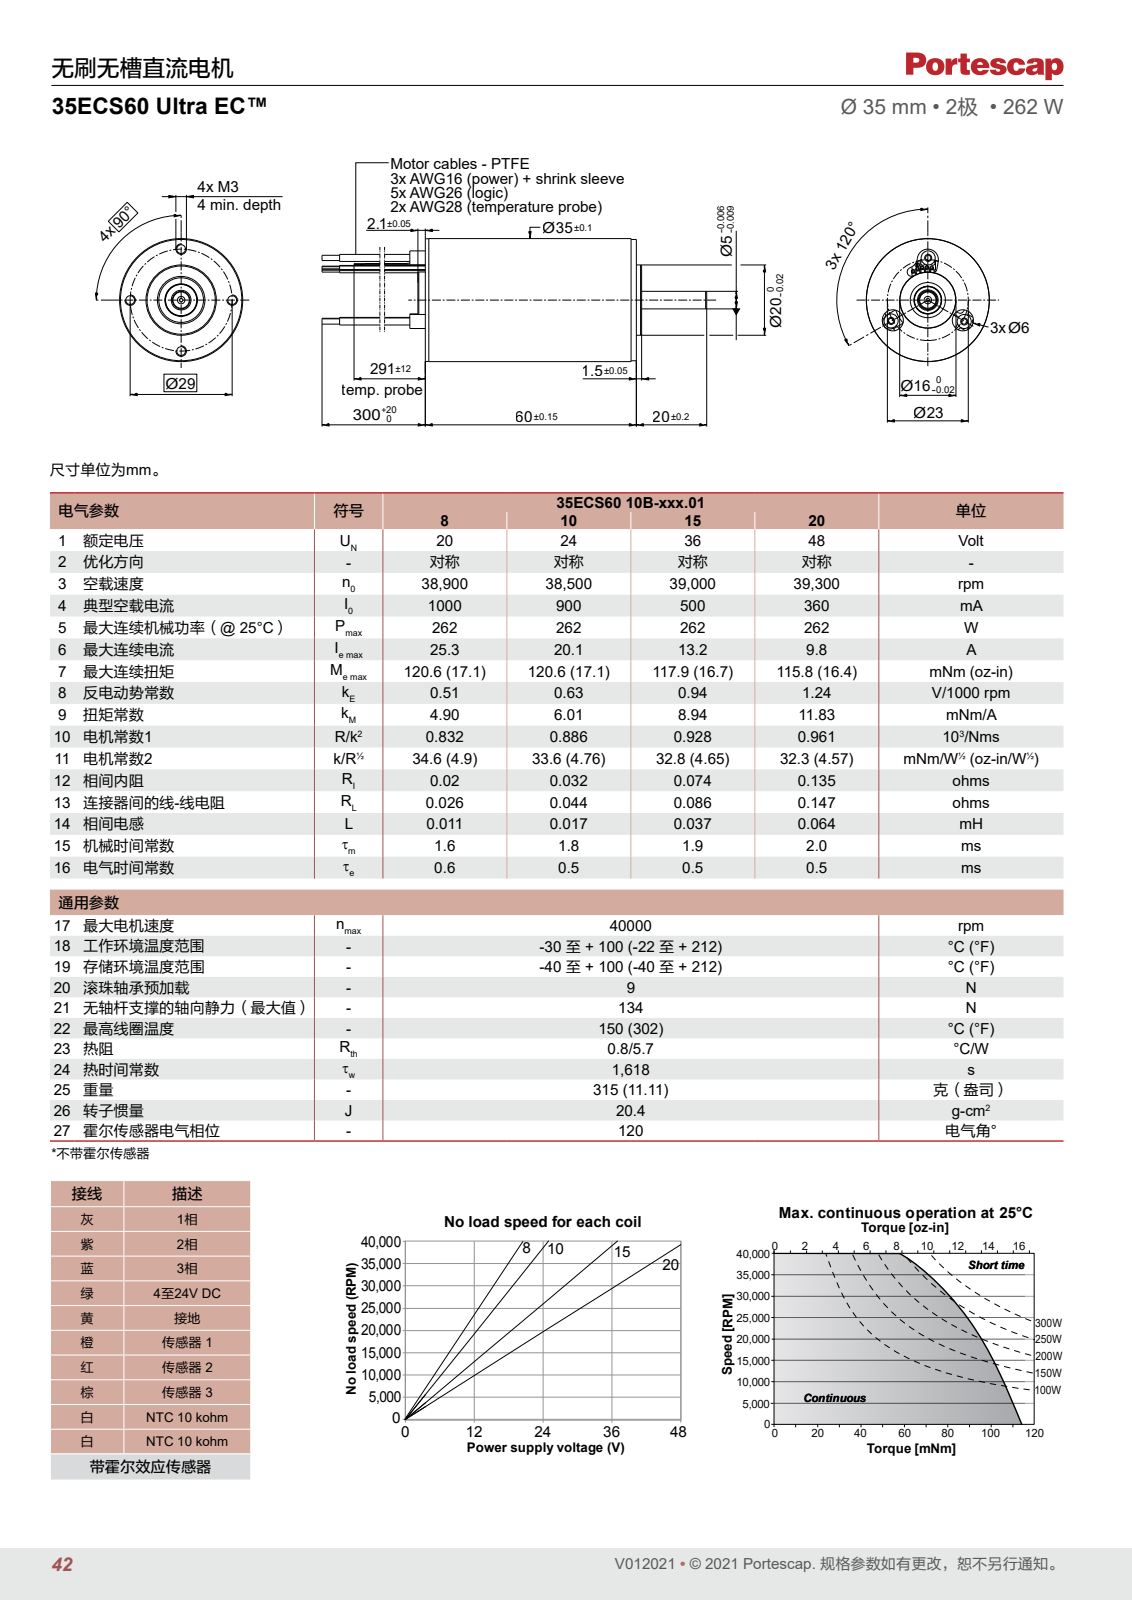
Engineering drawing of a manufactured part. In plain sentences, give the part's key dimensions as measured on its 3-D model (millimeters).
The part is named "35ECS60". Its 3-D file was written by "SolidWorks 2018 (AUTOMOTIVE_DESIGN)". It is 1 solid with 164 faces: 46 planar, 79 cylindrical and 39 other. Overall it measures 379.9 by 35 by 35 millimeters. Its volume is 62 351 cubic millimeters and its surface area 21 132 square millimeters. Round holes: 4 of diameter 2.5, 2 of diameter 6, 1 of diameter 1, 1 of diameter 10, 1 of diameter 10.4, 1 of diameter 13.5, 1 of diameter 33.6. Round bosses or shafts: 5 of diameter 1, 5 of diameter 0.6, 3 of diameter 4, 3 of diameter 2, 3 of diameter 1.5, 2 of diameter 0.45, 2 of diameter 0.32, 2 of diameter 0.25. Partial cylindrical surfaces (rounded edges, fillets, slot ends): 2 of radius 3, 1 of radius 1, 1 of radius 1.25, 1 of radius 10.5. The main face-to-face distances are 60, 1, 1.5, 61.1, 59, 61.5, 2.1, 2.5, 5, 62.1. The hole center spacings are 14.5, 20.51, 7.33, 11.5, 13.26, 22.57, 25.13, 29.
